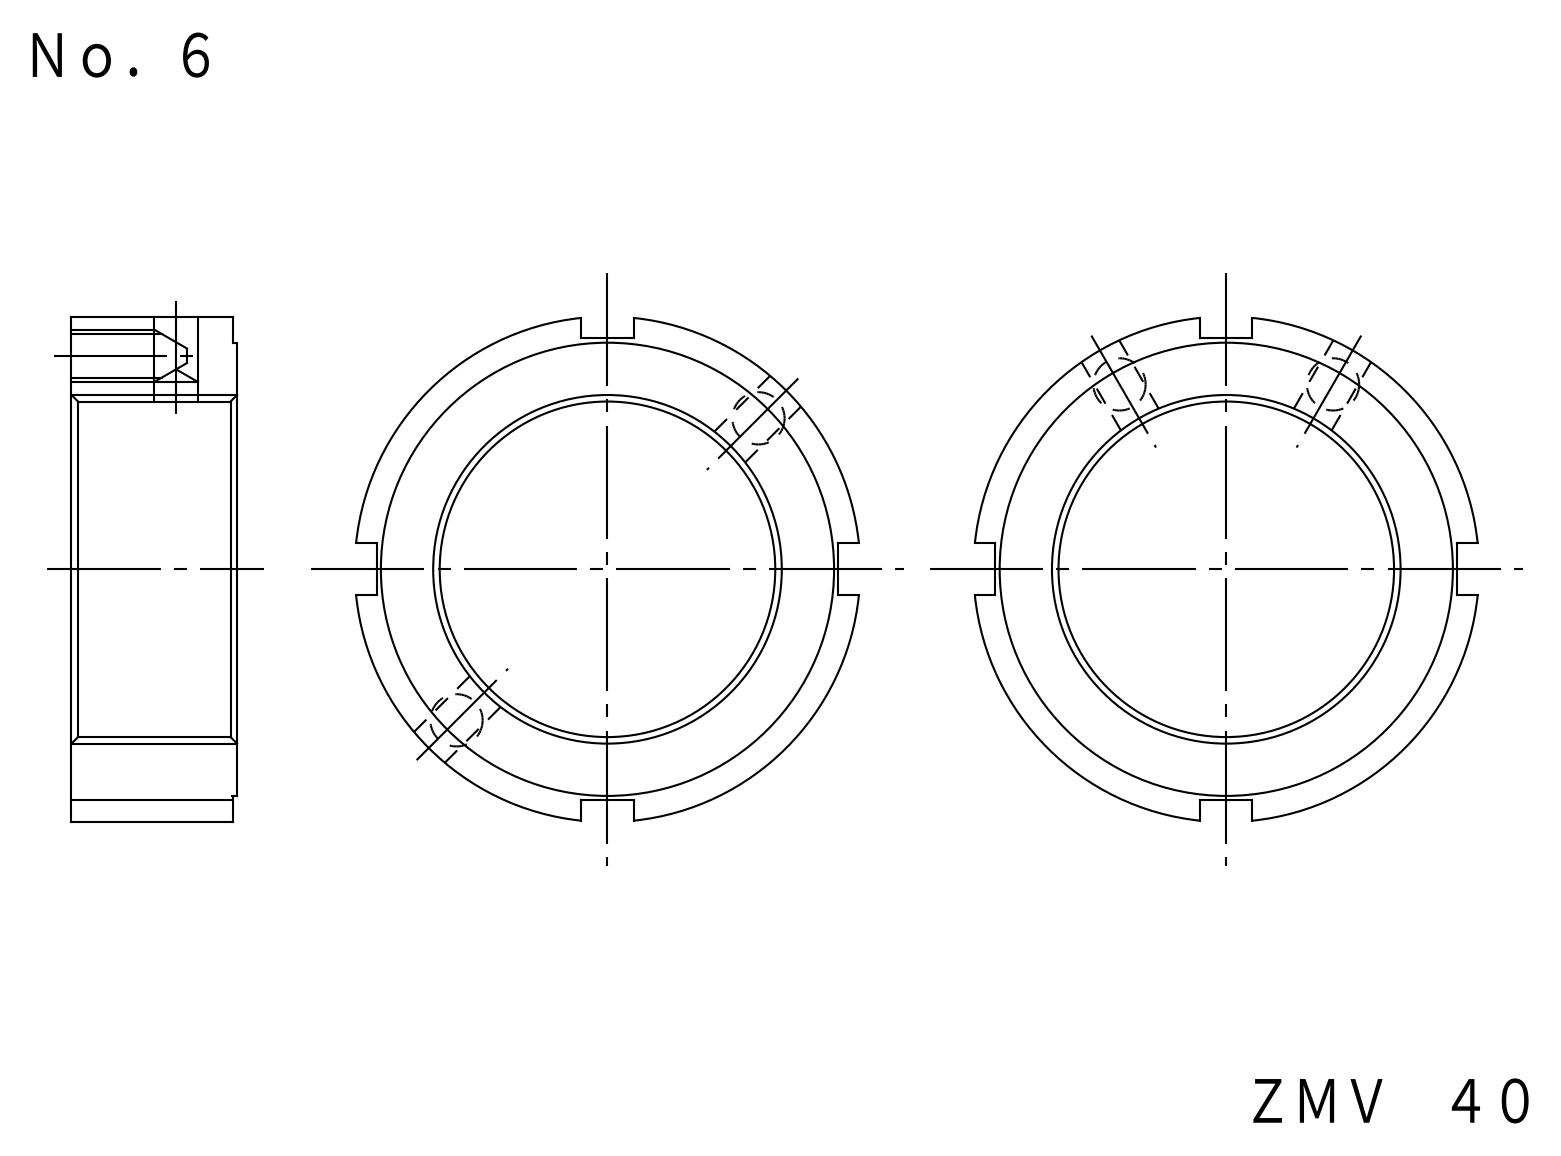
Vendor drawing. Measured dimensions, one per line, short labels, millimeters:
name: FKD ZMV40
written by: Autodesk Inventor LT (CONFIG_CONTROL_DESIGN)
unit: mm
bodies: 1 solid, 25 faces (15 planar, 10 cylindrical, 0 other)
size: 57.69 × 57.69 × 19
volume: 24 249 mm³; area: 9 279 mm²
holes: 2× ⌀4.92, 2× ⌀5, 1× ⌀40
bosses: 1× ⌀58, 1× ⌀52
face distances: 19, 0.5, 18.5, 23.5, 29.5, 53, 6
hole spacings: 24.49, 48.99
